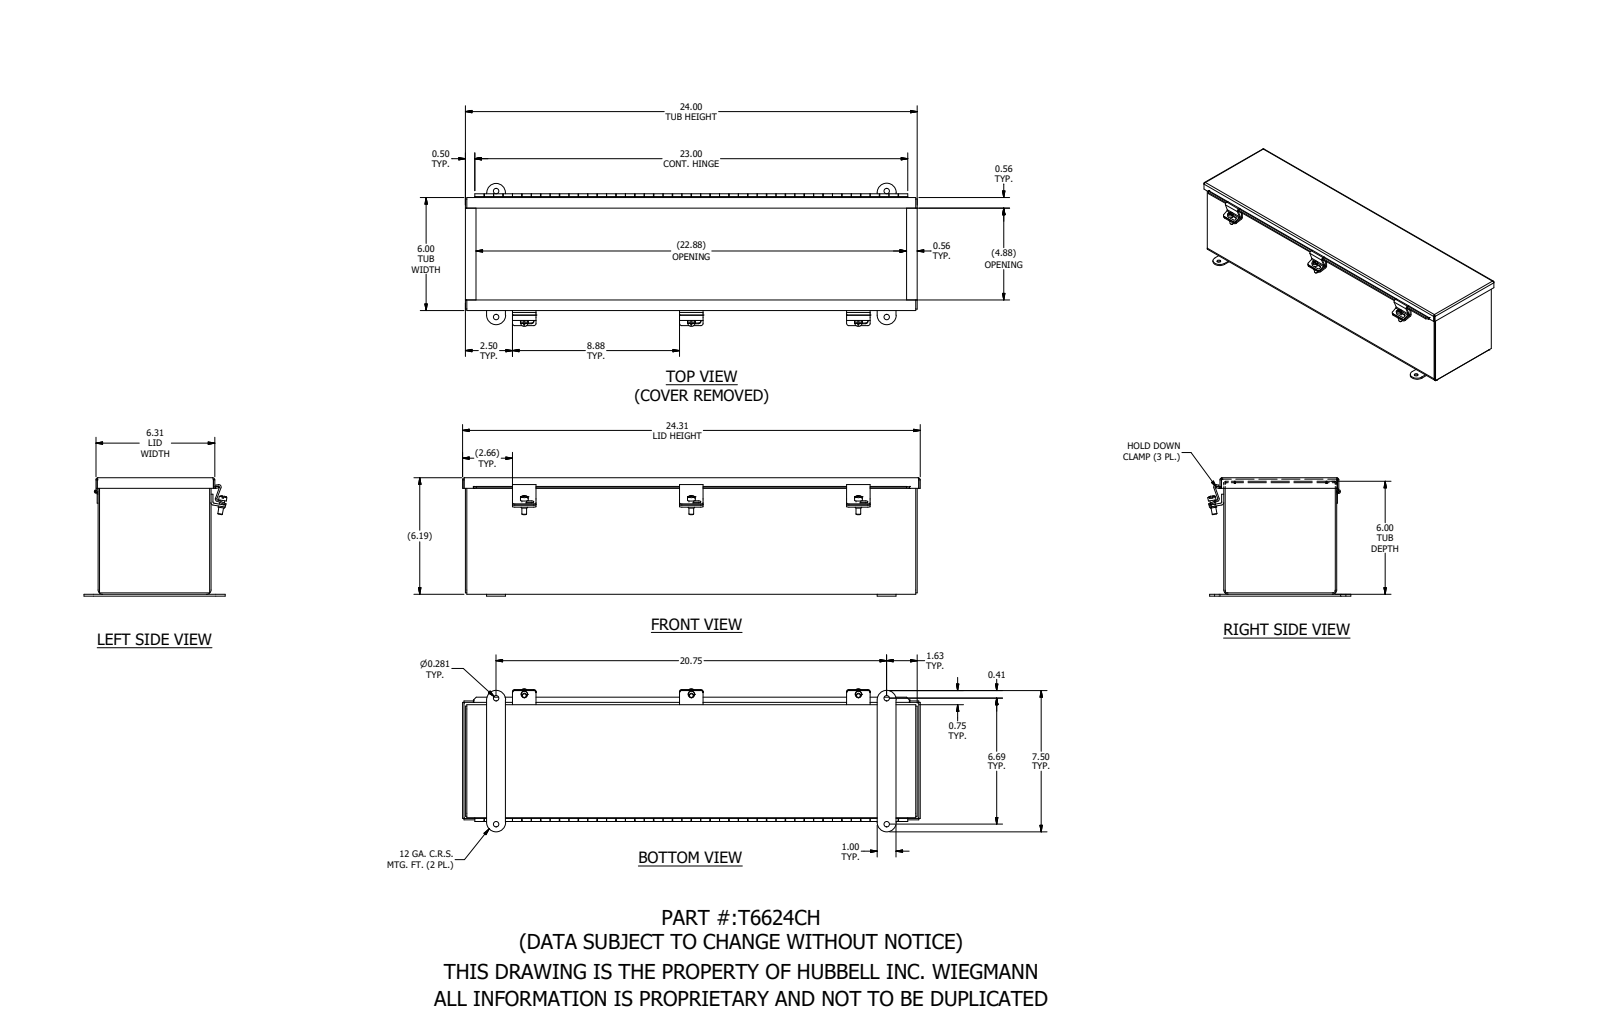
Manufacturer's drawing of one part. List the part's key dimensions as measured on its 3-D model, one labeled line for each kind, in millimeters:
Part name (STEP PRODUCT): T6624CH
STEP written by: SolidWorks 2021 (AUTOMOTIVE_DESIGN)
Units: millimetres
Bodies: 18 solids, 646 faces (338 planar, 285 cylindrical, 23 other)
Overall size (bounding box): 617.6 × 192.9 × 159.6
Volume: 918 200 mm³ · Surface area: 1 006 000 mm²
Round holes (diameter × count): ⌀7.1 ×4, ⌀5 ×3, ⌀2.9 ×1
Round bosses / shafts (diameter × count): ⌀10.4 ×3, ⌀8.7 ×3, ⌀6.4 ×3, ⌀5.1 ×1, ⌀2.5 ×1
Partial cylindrical surfaces — rounded edges, fillets, slot ends (radius × count): R3.2 ×12, R0.8 ×9, R2.7 ×9, R3.4 ×6, R12.7 ×4, R1.6 ×3, R3.2 ×3, R4 ×2
Main face-to-face distances: 1.9, 150.5, 155.3, 152.4, 148.6, 157.2, 153.4, 607.7, 4.8, 2.9
Hole centre spacings: 169.8, 527.1, 553.7, 225.4, 225.4, 450.9
